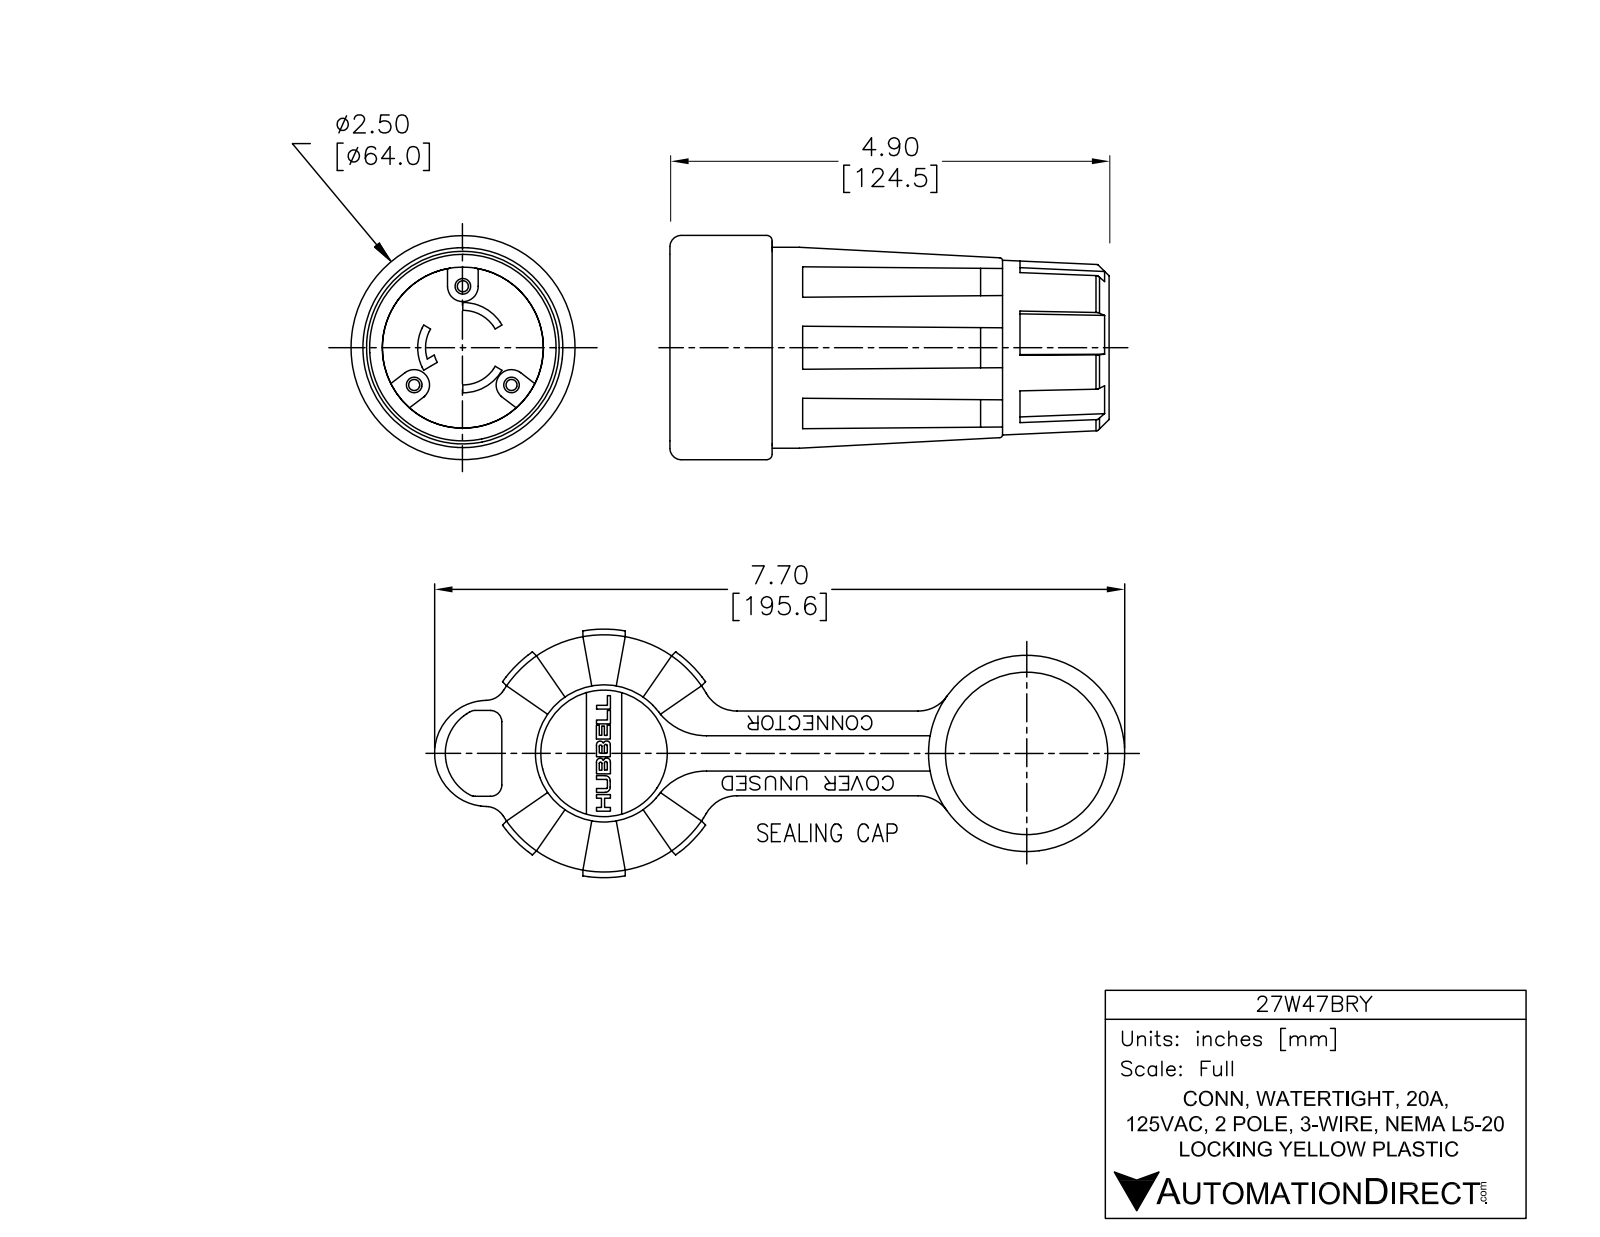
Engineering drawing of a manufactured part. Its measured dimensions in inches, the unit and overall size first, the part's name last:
Units: inches
Overall size (bounding box): 8.08 × 4.966 × 3.139
Round holes (diameter × count): ⌀0.95 ×1, ⌀1.82 ×1, ⌀1.86 ×1, ⌀2.345 ×1, ⌀2.805 ×1
Round bosses / shafts (diameter × count): ⌀0.2 ×3, ⌀2.76 ×1, ⌀2.755 ×1, ⌀2.43 ×1, ⌀2.25 ×1, ⌀1.975 ×1, ⌀1.415 ×1
Partial cylindrical surfaces — rounded edges, fillets, slot ends (radius × count): R0.015 ×16, R0.061 ×8, R0.25 ×6, R1.57 ×6, R0.11 ×3, R0.1 ×2, R0.359 ×1, R0.4 ×1
Main face-to-face distances: 0.08, 0.38, 0.67, 0.75, 0.06, 0.81, 0.14, 0.13, 2.685, 2.555
Hole centre spacings: 4.7
Volume: 20.17 in³ · Surface area: 104.5 in²
Bodies: 1 solid, 372 faces (144 planar, 99 cylindrical, 129 other)
Part name (STEP PRODUCT): 27W47BRY
STEP written by: SolidWorks 2013 (AUTOMOTIVE_DESIGN)
